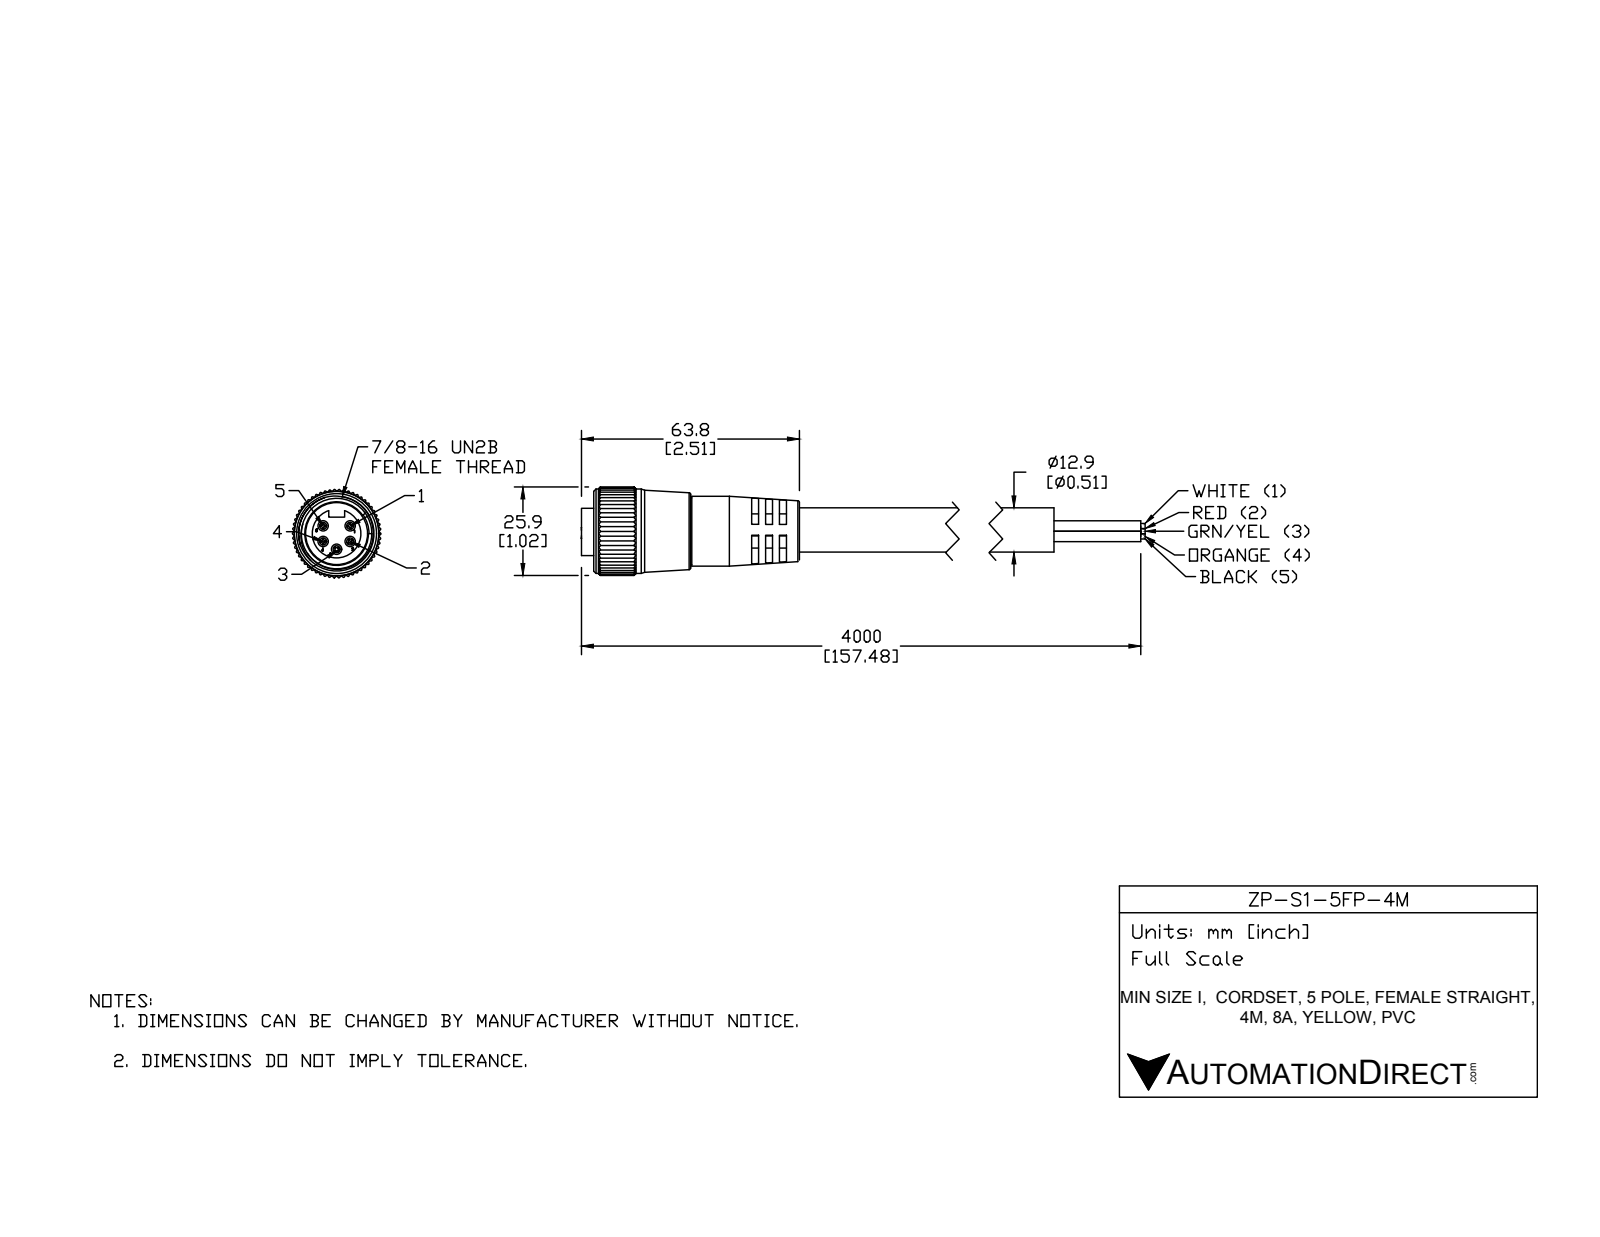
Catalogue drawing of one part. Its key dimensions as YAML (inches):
part_name: "ZP-S1-5FP-4M"
step_written_by: "SolidWorks 2015 (AUTOMOTIVE_DESIGN)"
units: inches
bodies: {solids: 2, faces: 576, planar: 216, cylindrical: 310, other: 50}
overall_size: [4.339, 2.083, 1.017]
volume: 1.867
surface_area: 19.41
round_holes:
  - {diameter: 0.12, count: 5}
  - {diameter: 0.714, count: 1}
  - {diameter: 0.81, count: 1}
  - {diameter: 0.827, count: 1}
round_bosses_or_shafts:
  - {diameter: 0.509, count: 2}
  - {diameter: 0.972, count: 1}
  - {diameter: 0.803, count: 1}
  - {diameter: 0.768, count: 1}
  - {diameter: 0.56, count: 1}
partial_cylinders:
  - {radius: 0.01, count: 165}
  - {radius: 0.207, count: 1}
  - {radius: 0.509, count: 1}
face_to_face_distances: [0.159, 0.079, 0.08, 0.237, 0.317, 0.239, 0.832, 0.911, 0.991, 1.069]
hole_center_spacings: [0.18, 0.312, 0.18, 0.36]
